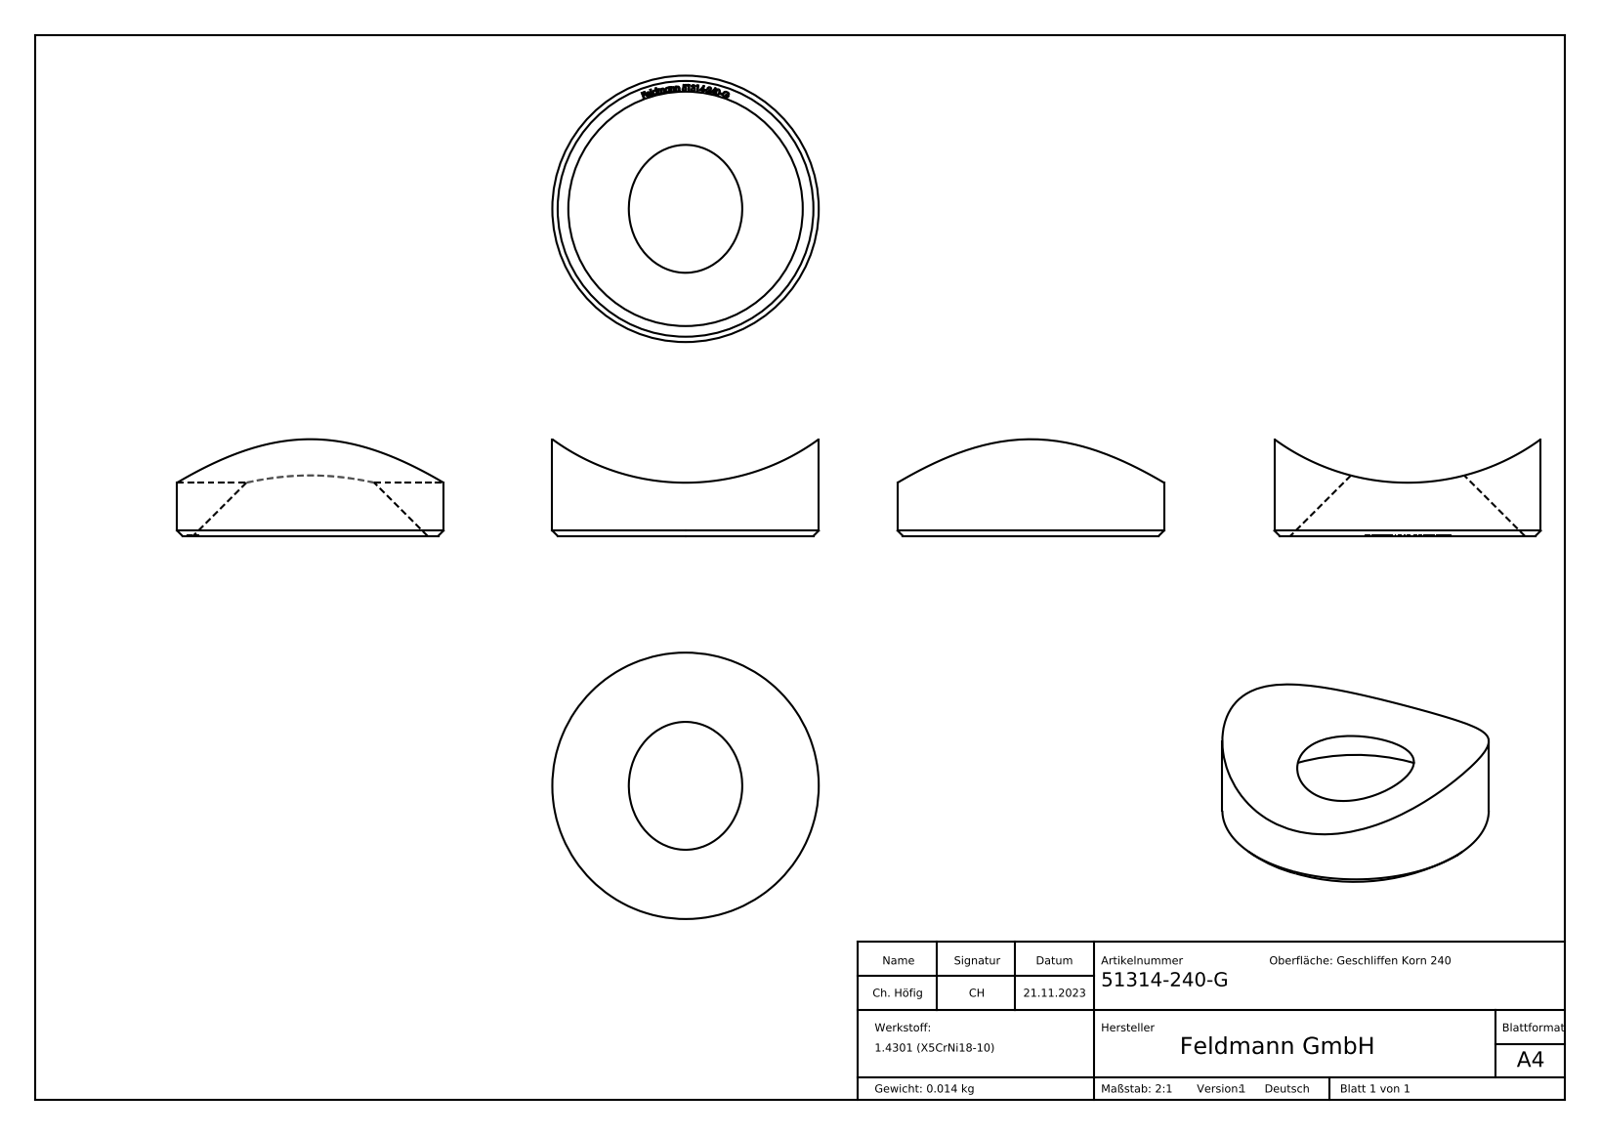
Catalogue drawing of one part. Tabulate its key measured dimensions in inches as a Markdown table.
| quantity | value |
| --- | --- |
| part name | 51314-240-G |
| STEP written by | SolidWorks 2018 (CONFIG_CONTROL_DESIGN) |
| units | inches |
| bodies | 1 solid, 243 faces (145 planar, 2 cylindrical, 96 other) |
| overall size | 0.984 × 0.984 × 0.357 |
| volume | 0.106 in³ |
| surface area | 2.248 in² |
| round bosses / shafts (diameter × count) | 0.984 × 1 |
| partial cylindrical surfaces (radius × count) | 0.835 × 1 |
| main face-to-face distances | 0.013, 0.012, 0.015, 0.014, 0.021, 0.019, 0.022, 0.015, 0.021, 0.017 |
